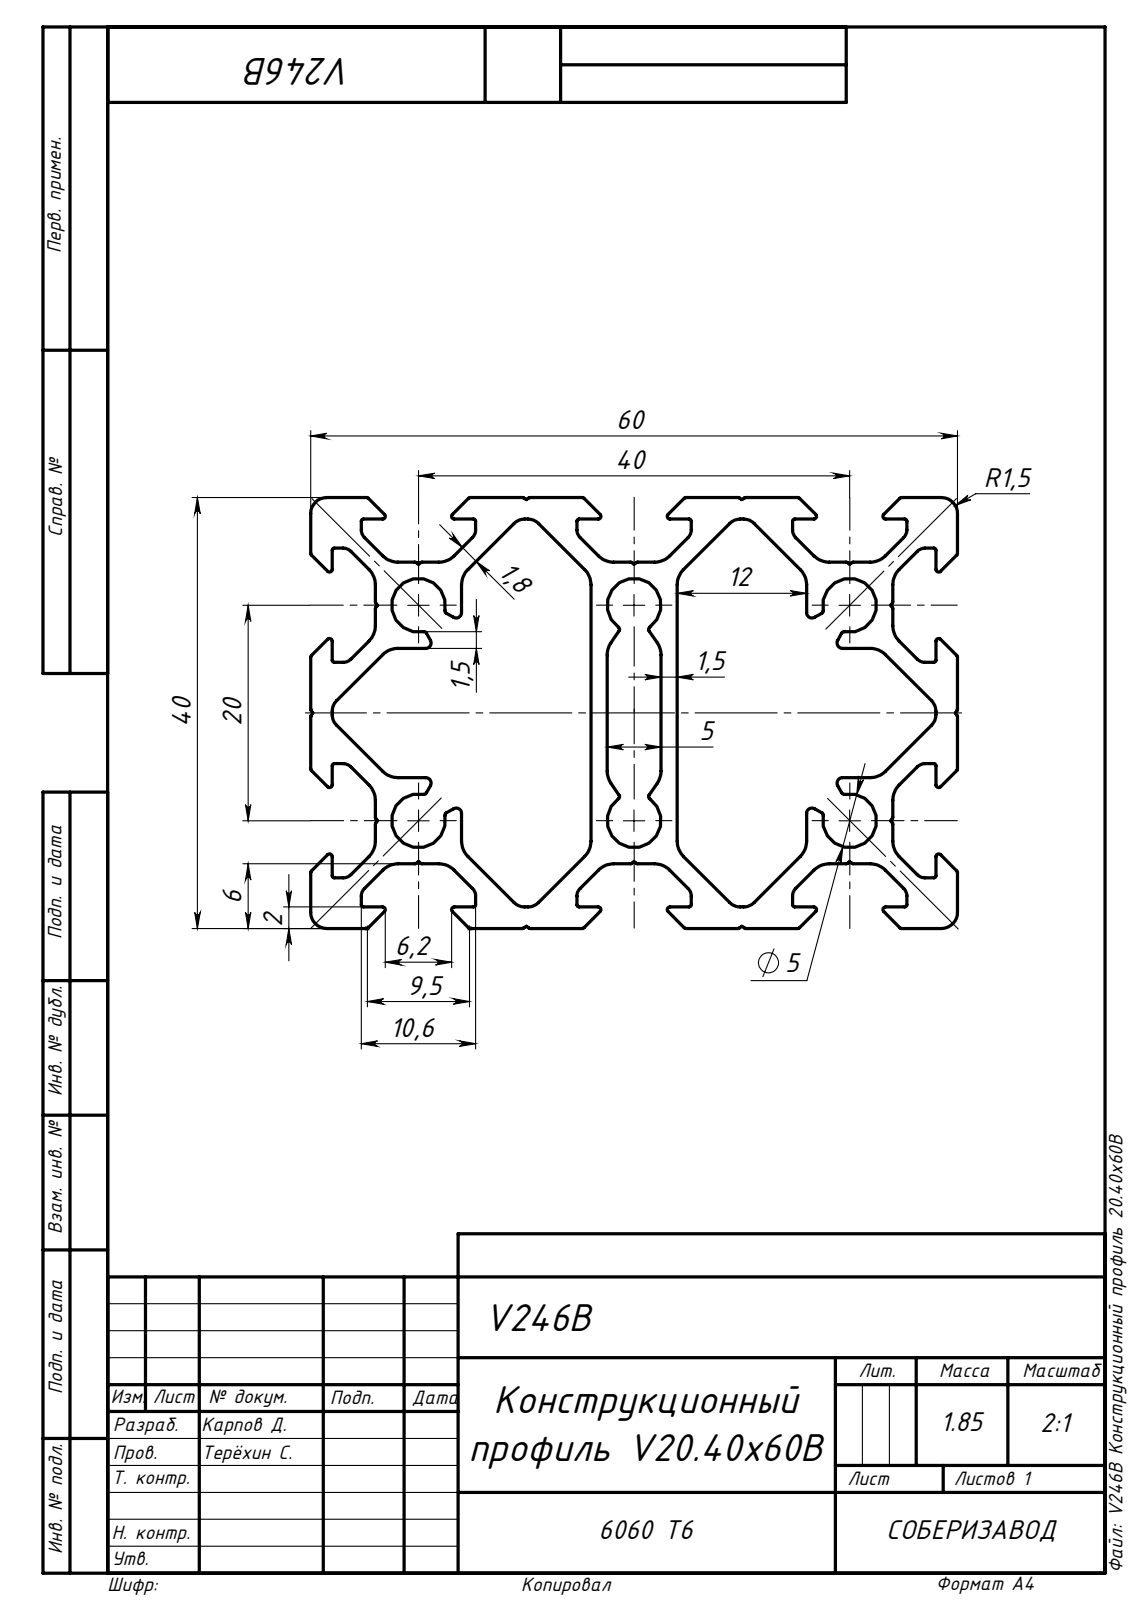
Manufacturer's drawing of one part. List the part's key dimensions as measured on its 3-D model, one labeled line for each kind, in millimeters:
STEP written by: SolidWorks 2019 (AUTOMOTIVE_DESIGN)
Units: millimetres
Bodies: 1 solid, 414 faces (196 planar, 218 cylindrical, 0 other)
Overall size (bounding box): 1000 × 60 × 40
Volume: 684 821 mm³ · Surface area: 654 227 mm²
Round holes (diameter × count): ⌀5 ×6
Partial cylindrical surfaces — rounded edges, fillets, slot ends (radius × count): R0.25 ×84, R2 ×36, R0.2 ×20, R1 ×20, R1.4 ×12, R0.5 ×8, R1.5 ×4
Main face-to-face distances: 14.14, 34, 28.28, 8, 26, 20, 2.83, 4.63, 16.97, 18.77
Hole centre spacings: 20, 28.28, 40, 44.72
